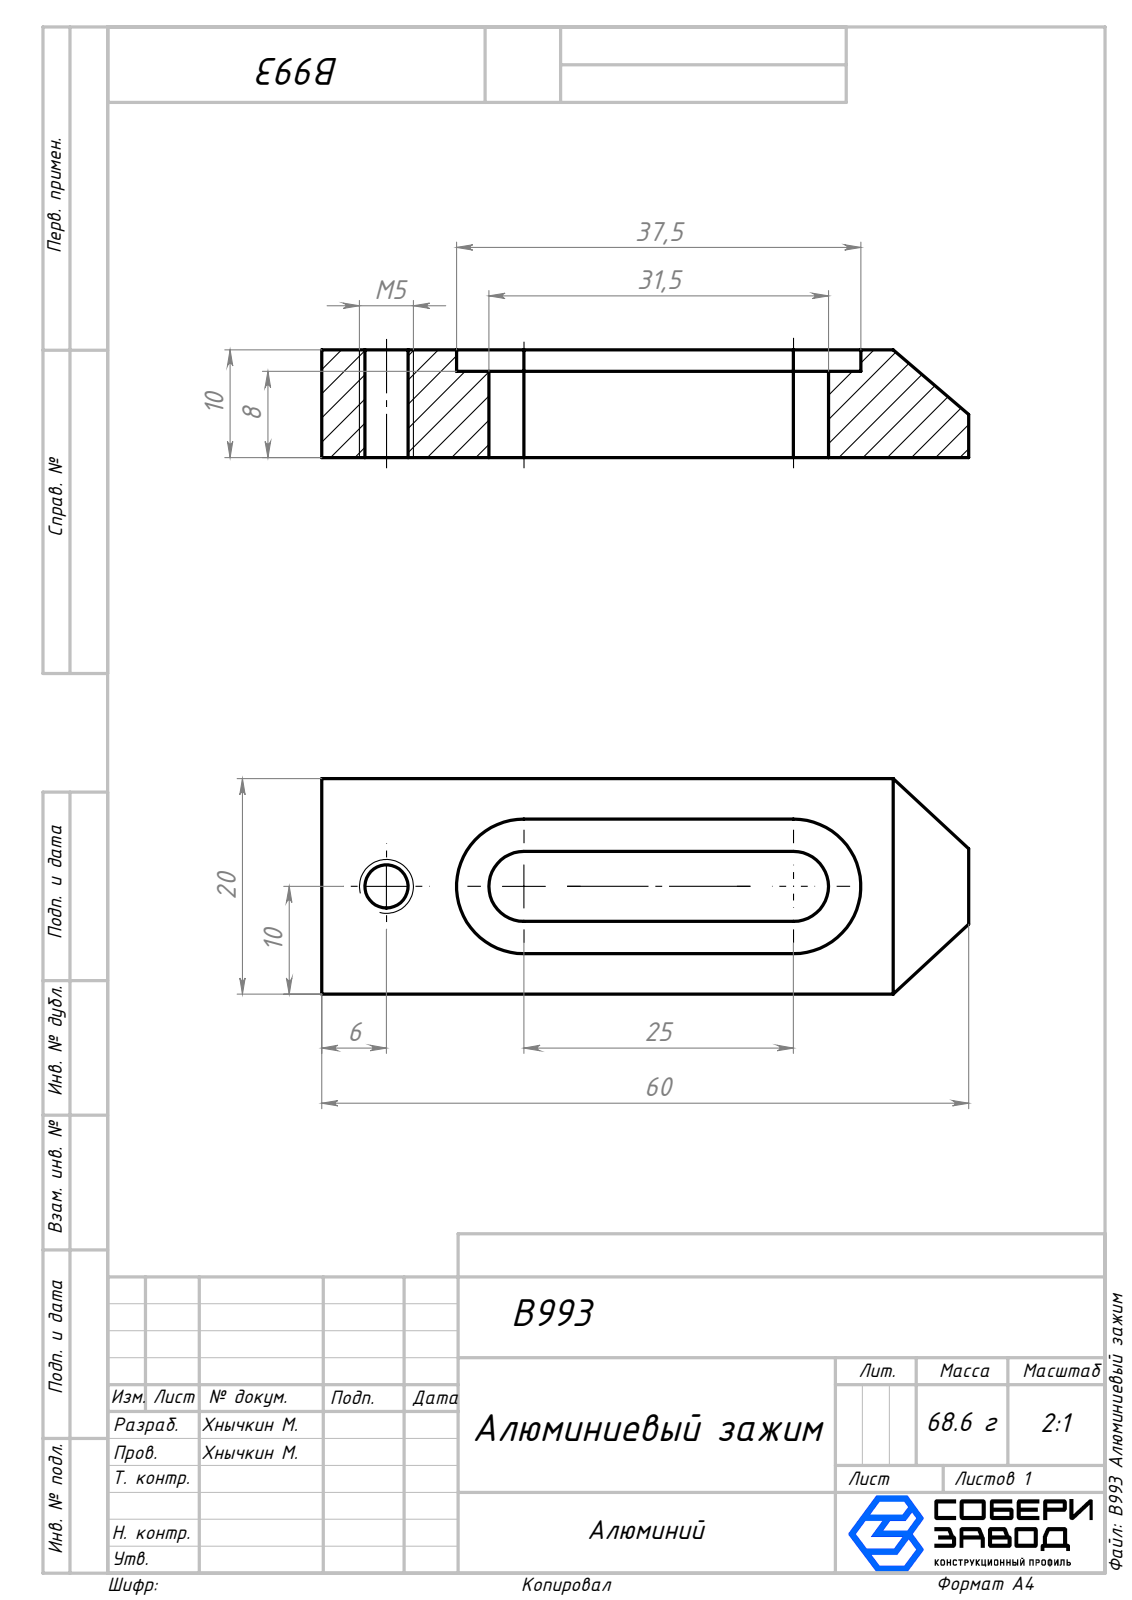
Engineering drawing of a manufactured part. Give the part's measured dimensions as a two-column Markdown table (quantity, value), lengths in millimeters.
| quantity | value |
| --- | --- |
| part name | B993 Алюминиевый зажим |
| STEP written by | SolidWorks 2026 (AUTOMOTIVE_DESIGN) |
| units | millimeters |
| bodies | 1 solid, 20 faces (14 planar, 6 cylindrical, 0 other) |
| overall size | 60 × 20 × 10 |
| volume | 8 745 mm³ |
| surface area | 4 212 mm² |
| round holes (diameter × count) | 4 × 1 |
| partial cylindrical surfaces (radius × count) | 3.25 × 2, 6.25 × 2 |
| main face-to-face distances | 10, 20, 6.75, 13.25, 8, 2, 6.5, 3.75, 16.25, 3 |
